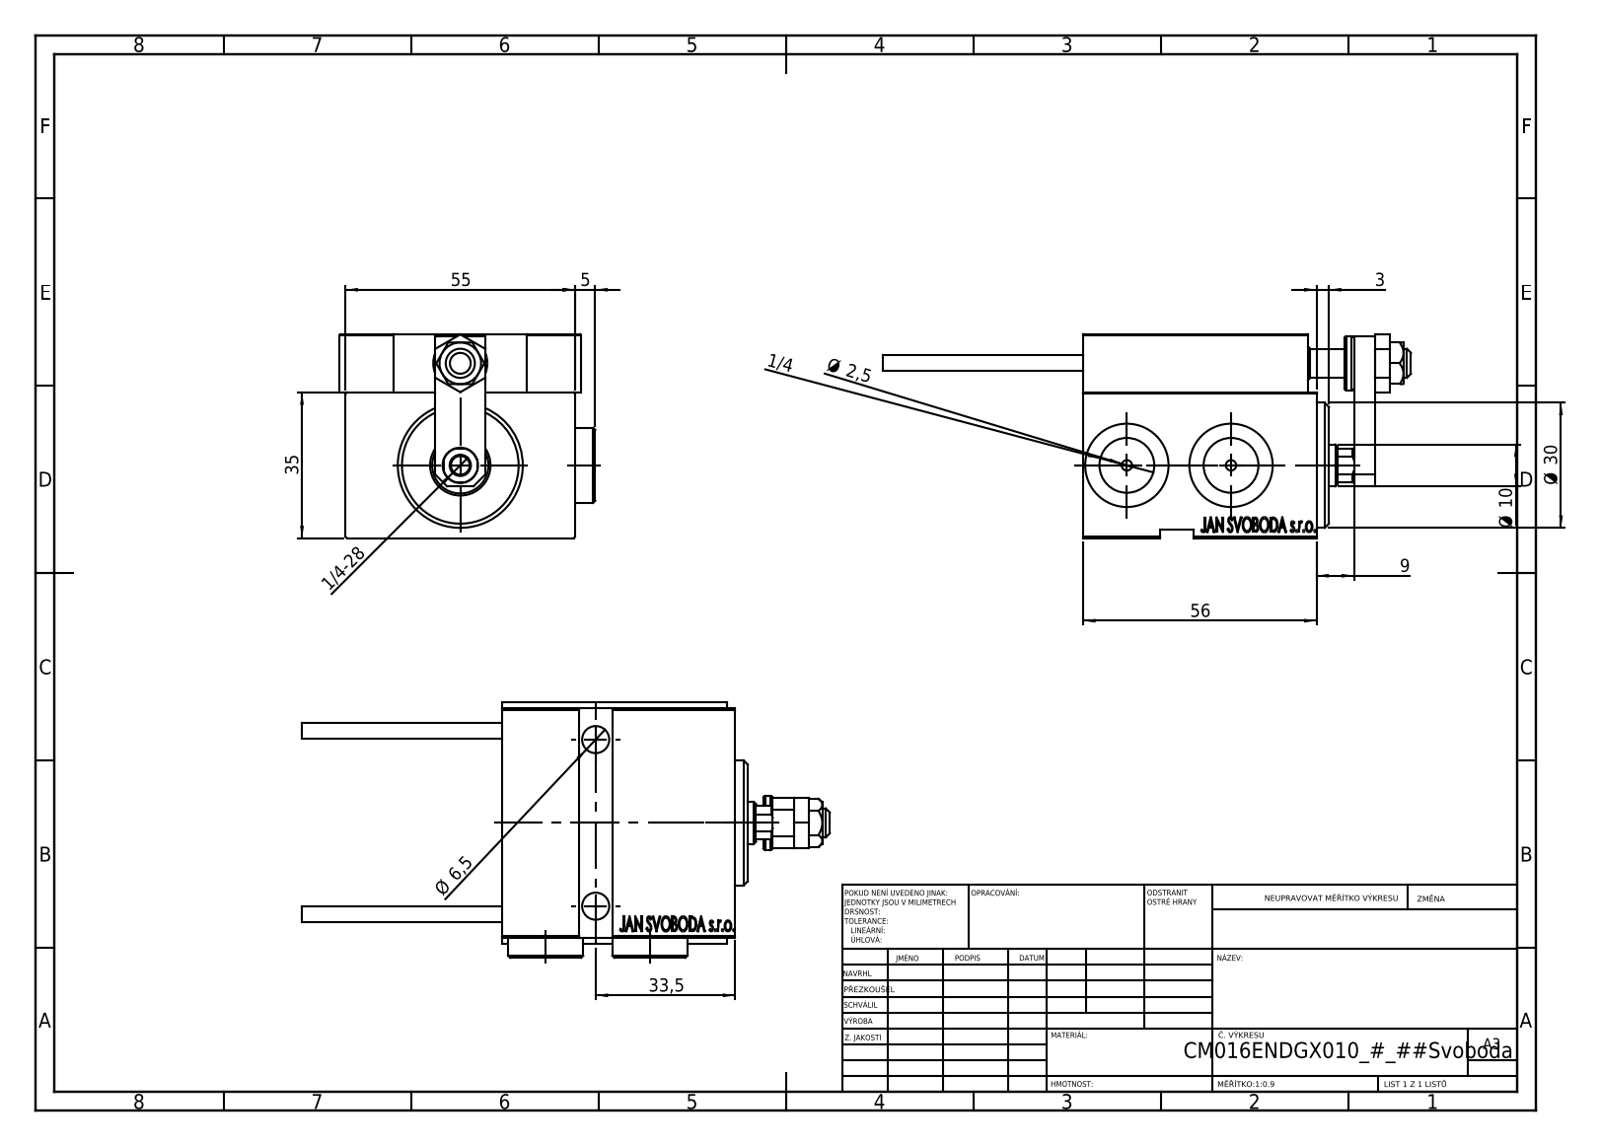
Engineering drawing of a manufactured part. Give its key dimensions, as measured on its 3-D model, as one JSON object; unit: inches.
{"part_name": "V450CM_E_VCP; V450CM_VC_B; SWITCH DIM B,W; TYC_L79 (+7 more)", "step_written_by": "SolidWorks 2019 (CONFIG_CONTROL_DESIGN)", "units": "inches", "bodies": {"solids": 26, "faces": 1340, "planar": 603, "cylindrical": 192, "other": 545}, "overall_size": [4.988, 2.417, 1.929], "volume_in3": 8.699, "surface_area_in2": 77.62, "round_holes": [[0.315, 5], [0.126, 4], [0.157, 4], [0.098, 2], [0.197, 2], [0.256, 2], [0.413, 2], [0.518, 2], [0.787, 2], [0.177, 1], [0.276, 1], [0.335, 1]], "round_bosses_or_shafts": [[0.709, 3], [0.197, 2], [0.15, 2], [1.181, 1], [0.512, 1], [0.433, 1]], "partial_cylinders_radius": [[0.012, 26], [0.118, 2], [0.177, 1]], "face_to_face_distances": [0.551, 1.378, 1.929, 0.197, 0.059, 0.394, 0.118, 2.165, 0.276, 2.205], "hole_center_spacings": [0.794, 0.325, 0.448, 0.787, 0.922, 1.115, 1.165, 1.169]}
